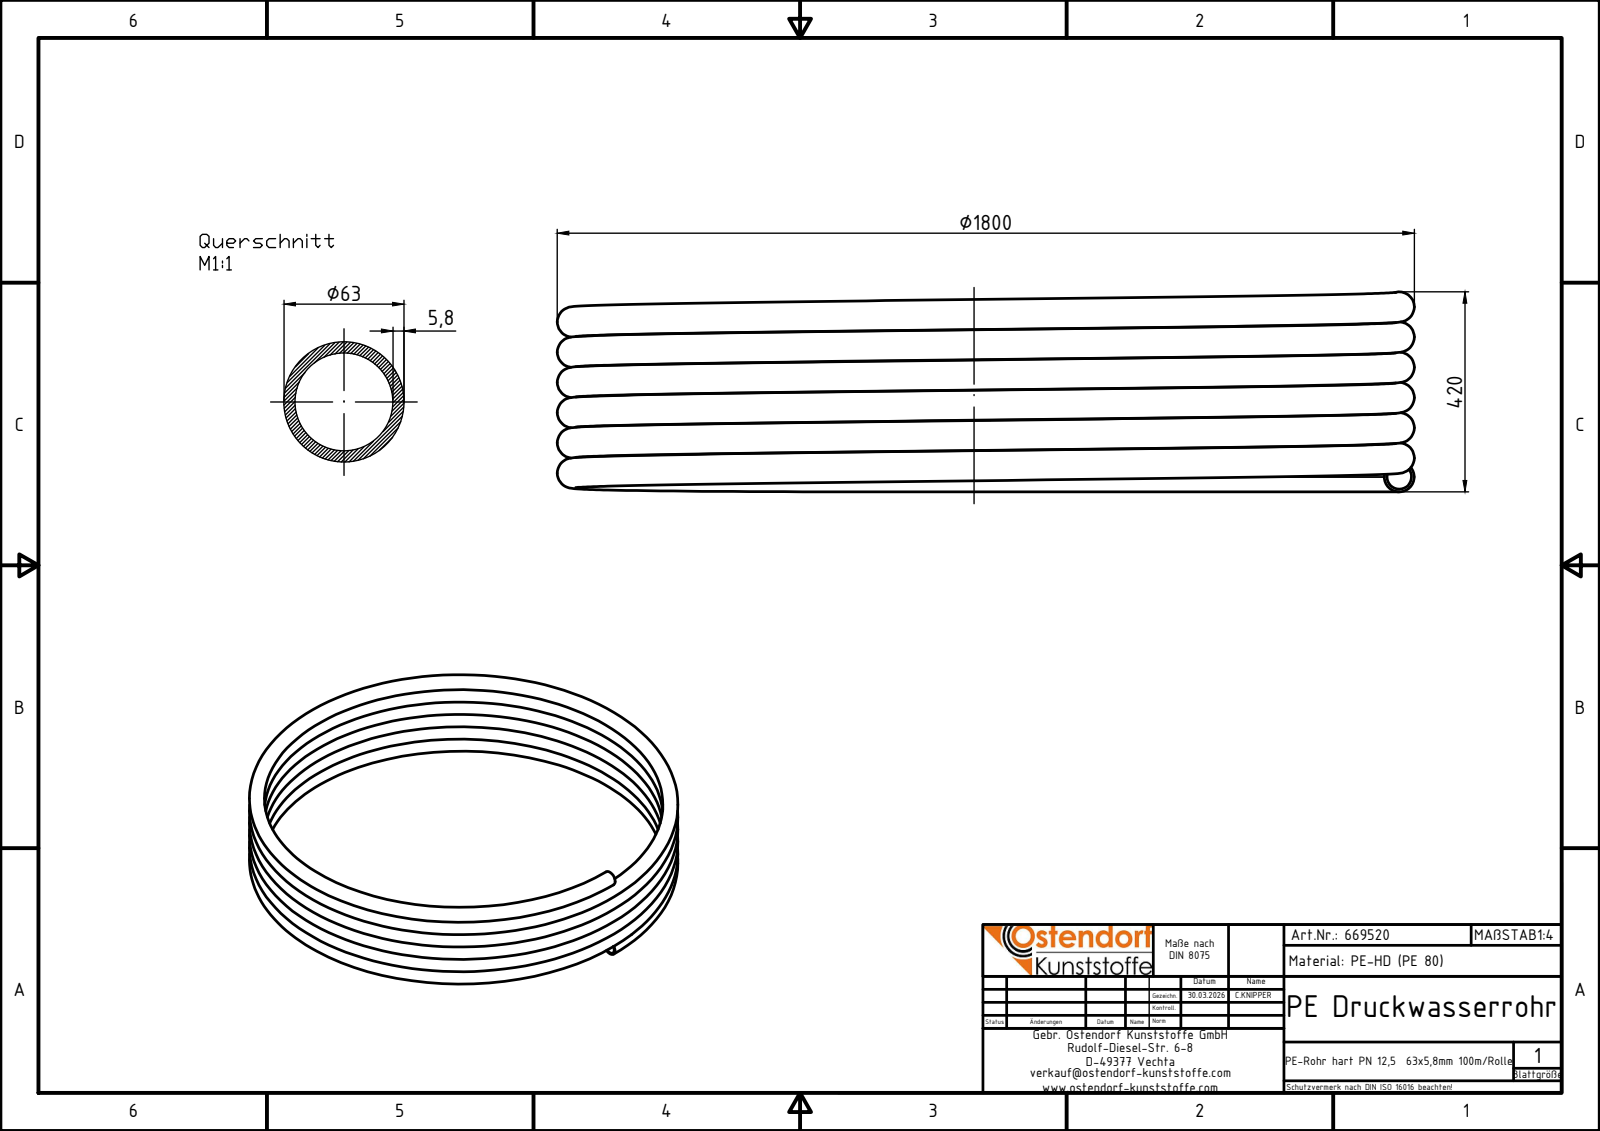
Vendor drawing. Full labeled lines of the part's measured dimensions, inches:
Part name (STEP PRODUCT): 669520z
STEP written by: Autodesk Inventor 2024 (AUTOMOTIVE_DESIGN)
Units: inches
Bodies: 1 solid, 7 faces (3 planar, 0 cylindrical, 4 other)
Overall size (bounding box): 70.866 × 70.866 × 16.543
Volume: 2 028 in³ · Surface area: 17 930 in²
